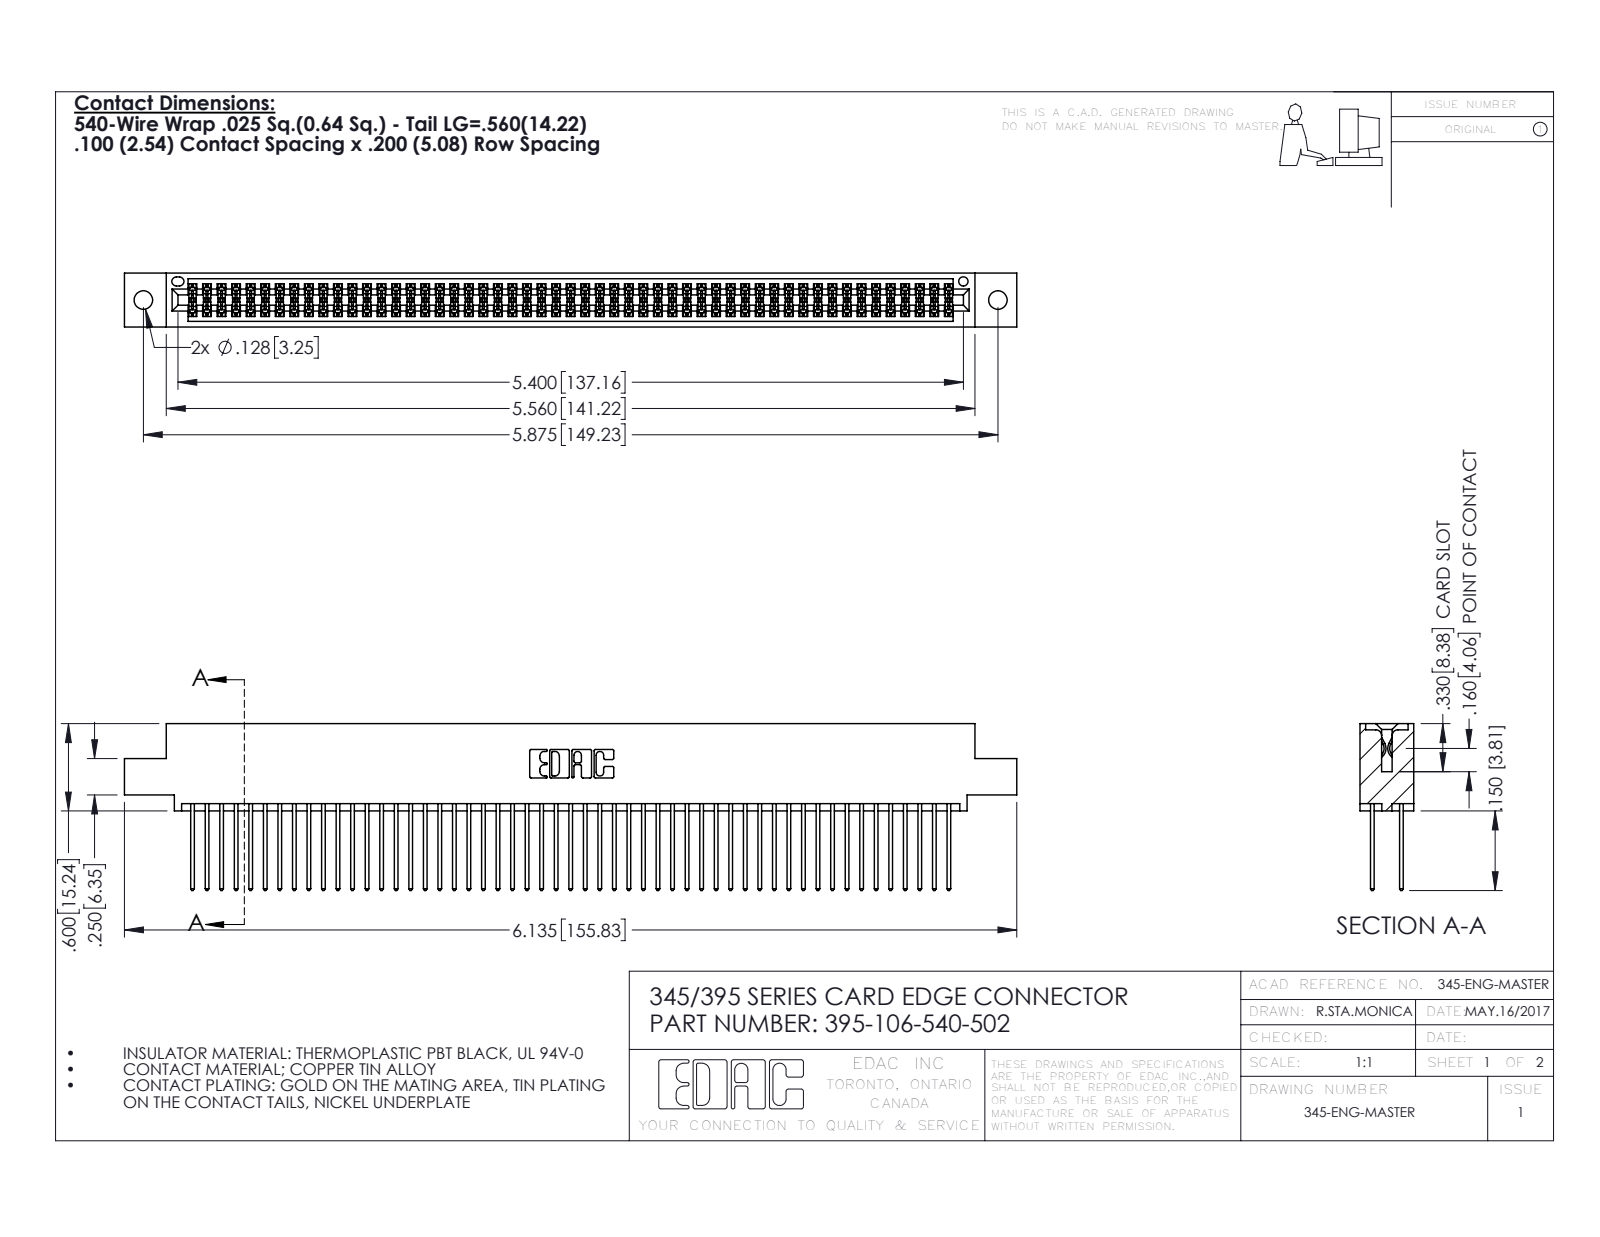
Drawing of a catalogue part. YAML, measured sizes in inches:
part_name: "345-292-001_345-293-140; 345 Part_0.110 Offset - 0.128 Dia; 395-106-540-502"
step_written_by: "SolidWorks 2016 (CONFIG_CONTROL_DESIGN)"
units: inches
bodies: {solids: 107, faces: 5430, planar: 3582, cylindrical: 1848, other: 0}
overall_size: [6.135, 1.147, 0.37]
volume: 0.948
surface_area: 38.53
round_holes:
  - {diameter: 0.128, count: 2}
  - {diameter: 0.064, count: 1}
partial_cylinders:
  - {radius: 0.006, count: 159}
  - {radius: 0.01, count: 106}
  - {radius: 0.01, count: 22}
  - {radius: 0.007, count: 6}
  - {radius: 0.031, count: 6}
  - {radius: 0.026, count: 3}
  - {radius: 0.014, count: 2}
  - {radius: 0.019, count: 2}
face_to_face_distances: [0.298, 0.072, 0.2, 0.098, 0.272, 0.025, 0.37, 0.225, 0.175, 0.149]
hole_center_spacings: [0.27, 5.639, 5.875]
